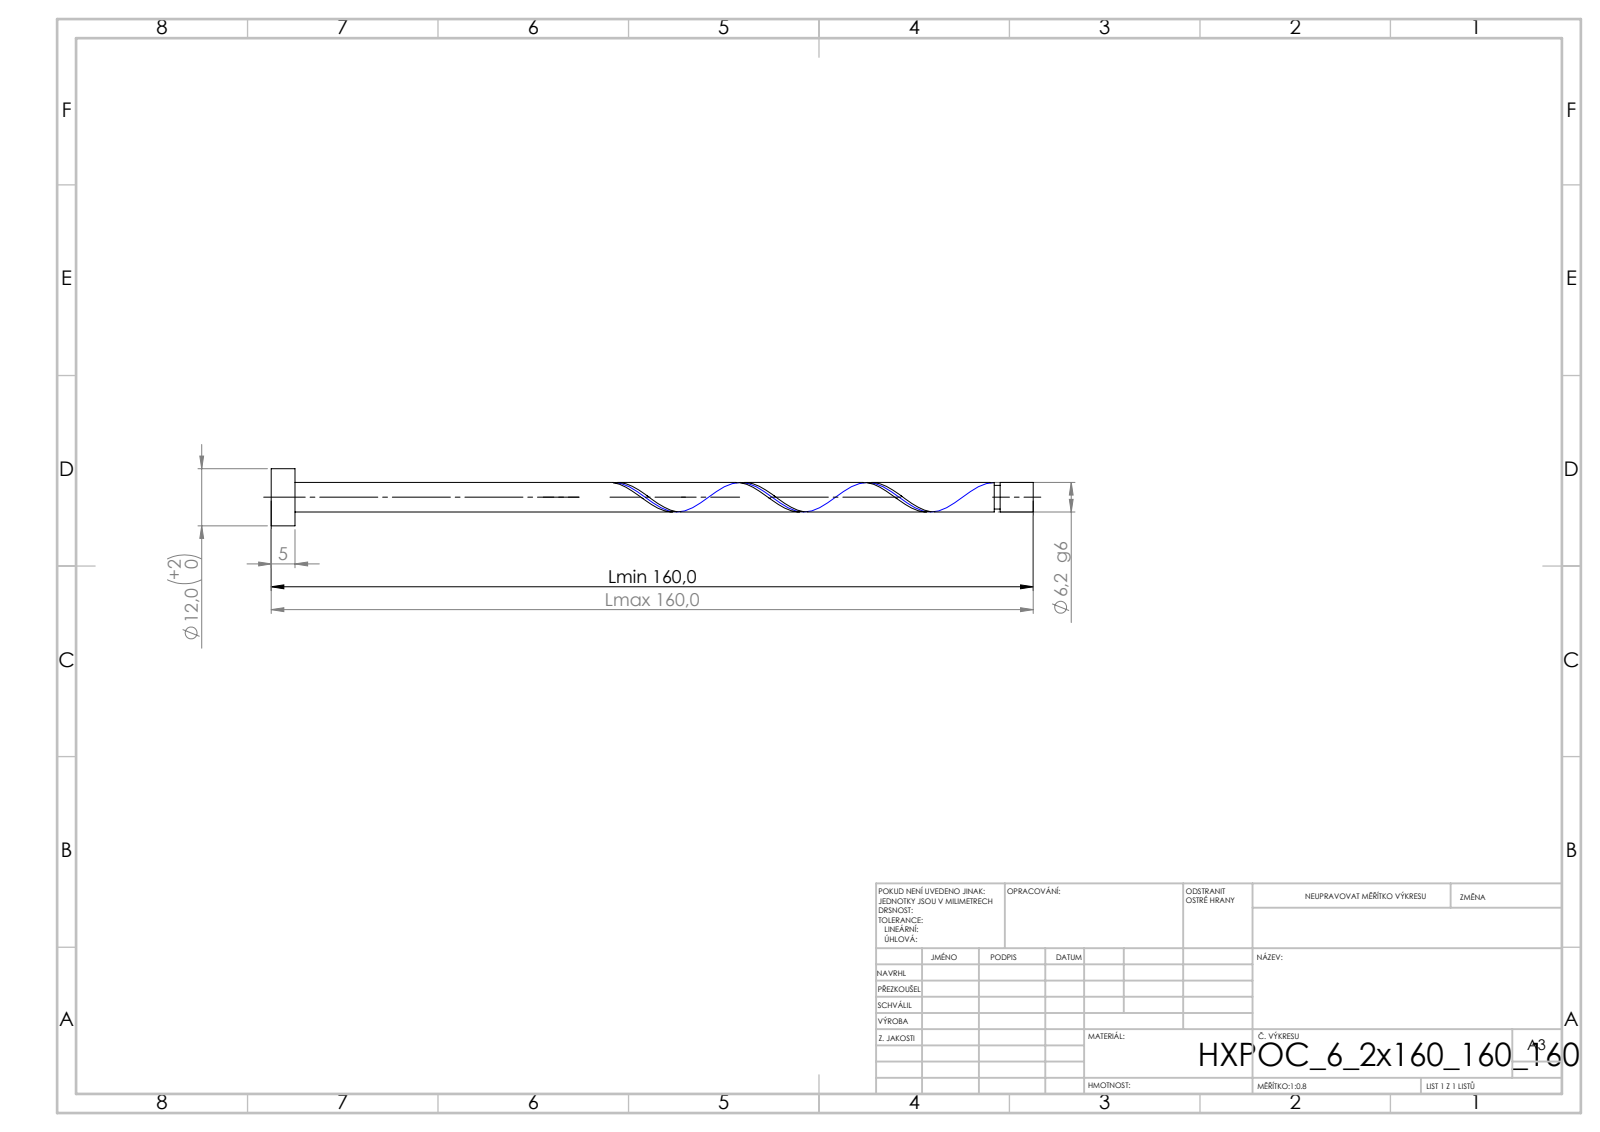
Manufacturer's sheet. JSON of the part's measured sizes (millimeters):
{"step_written_by": "SolidWorks 2019 (CONFIG_CONTROL_DESIGN)", "units": "millimeters", "bodies": {"solids": 1, "faces": 21, "planar": 6, "cylindrical": 14, "other": 1}, "overall_size": [160, 12, 12], "volume_mm3": 5185, "surface_area_mm2": 3514, "round_bosses_or_shafts": [[12, 1], [6.2, 1], [4.96, 1]], "face_to_face_distances": [5, 160, 155, 153.07, 148.07, 6.93, 151.83, 146.83, 1.24, 8.17]}
